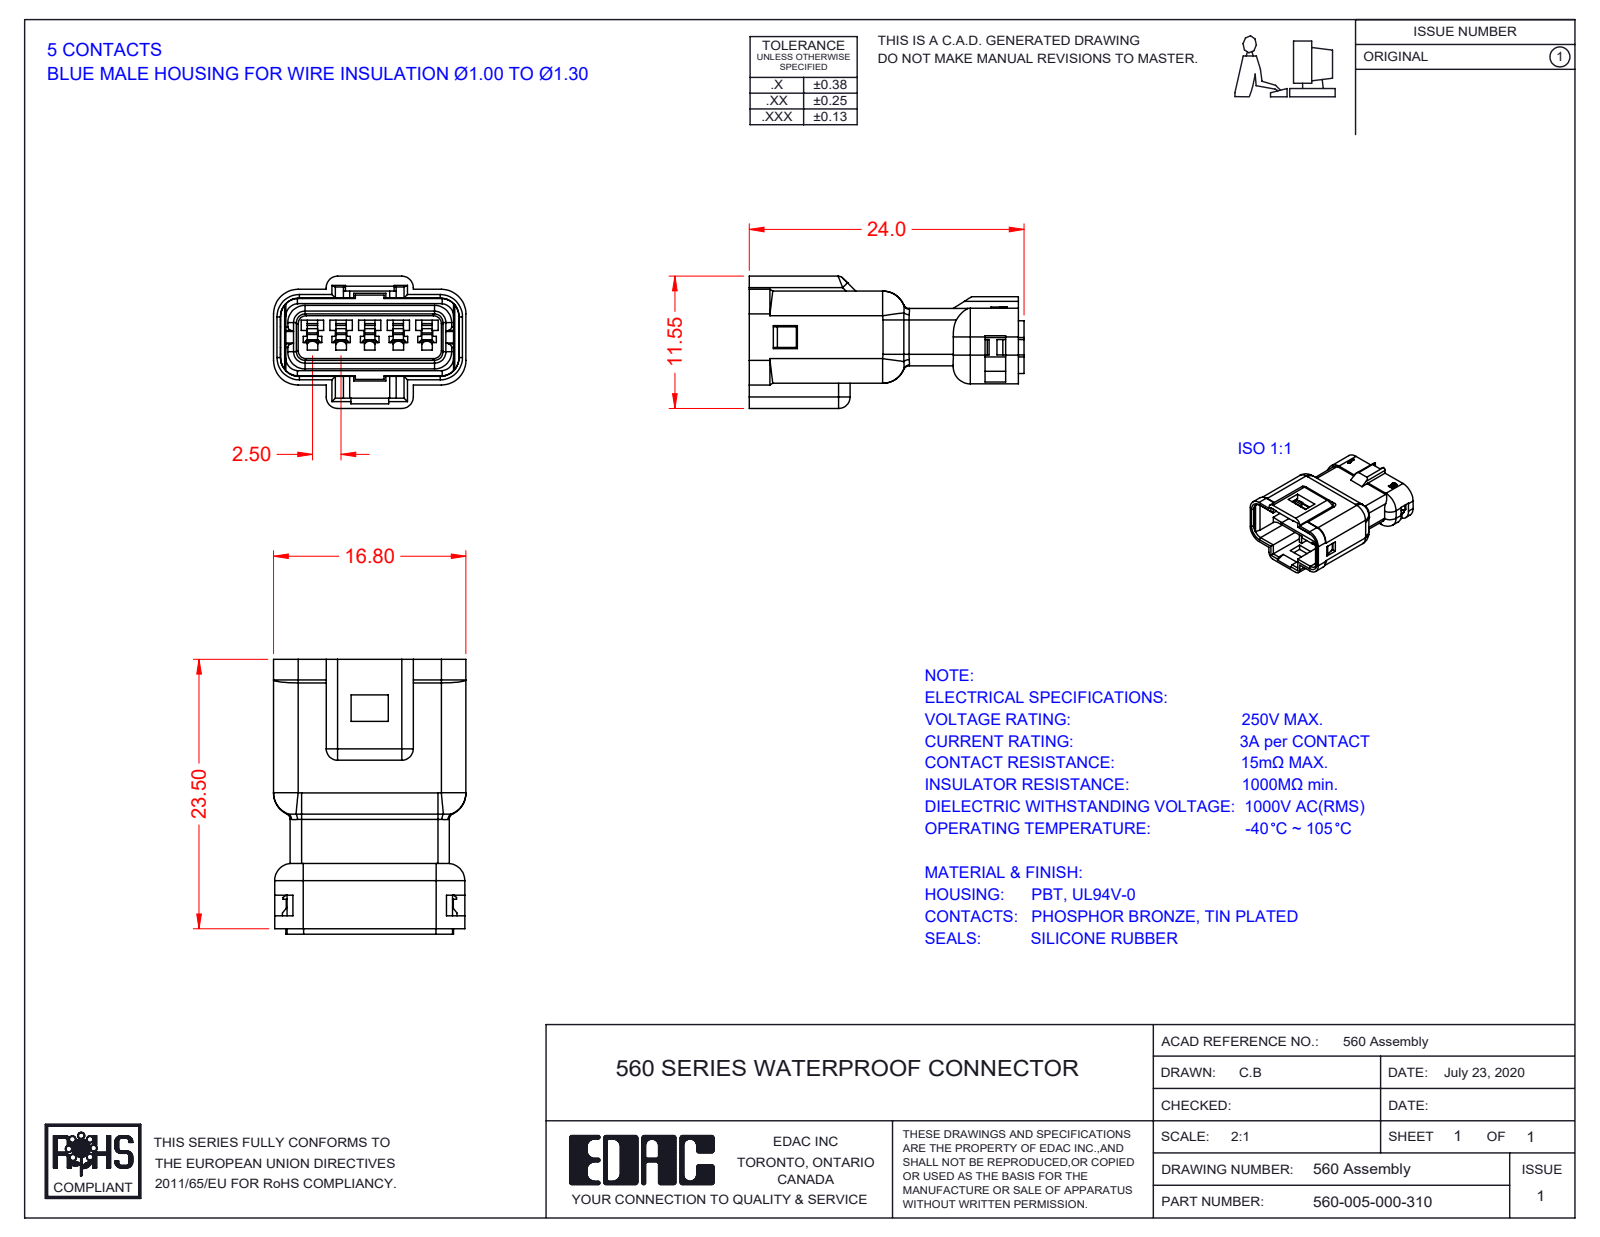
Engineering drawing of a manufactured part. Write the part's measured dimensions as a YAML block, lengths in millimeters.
part_name: "INTERNAL-WIRE-SEAL-5POS; FACIAL_SEAL_5POS; 560-005-000-310; REAR-INSULATOR-5POS (+2 more)"
step_written_by: "SolidWorks 2020 (CONFIG_CONTROL_DESIGN)"
units: millimeters
bodies: {solids: 5, faces: 1210, planar: 692, cylindrical: 241, other: 277}
overall_size: [23.98, 16.8, 11.55]
volume: 1561
surface_area: 4053
round_holes:
  - {diameter: 1.5, count: 5}
partial_cylinders:
  - {radius: 1, count: 25}
  - {radius: 0.25, count: 16}
  - {radius: 0.35, count: 13}
  - {radius: 1.2, count: 12}
  - {radius: 0.15, count: 9}
  - {radius: 1.5, count: 8}
  - {radius: 1.65, count: 8}
  - {radius: 2.15, count: 8}
face_to_face_distances: [0.6, 0.9, 4.7, 7.45, 3.8, 2.5, 0.8, 3.9, 6.85, 1.95]
hole_center_spacings: [2.5, 5, 7.5, 10]
